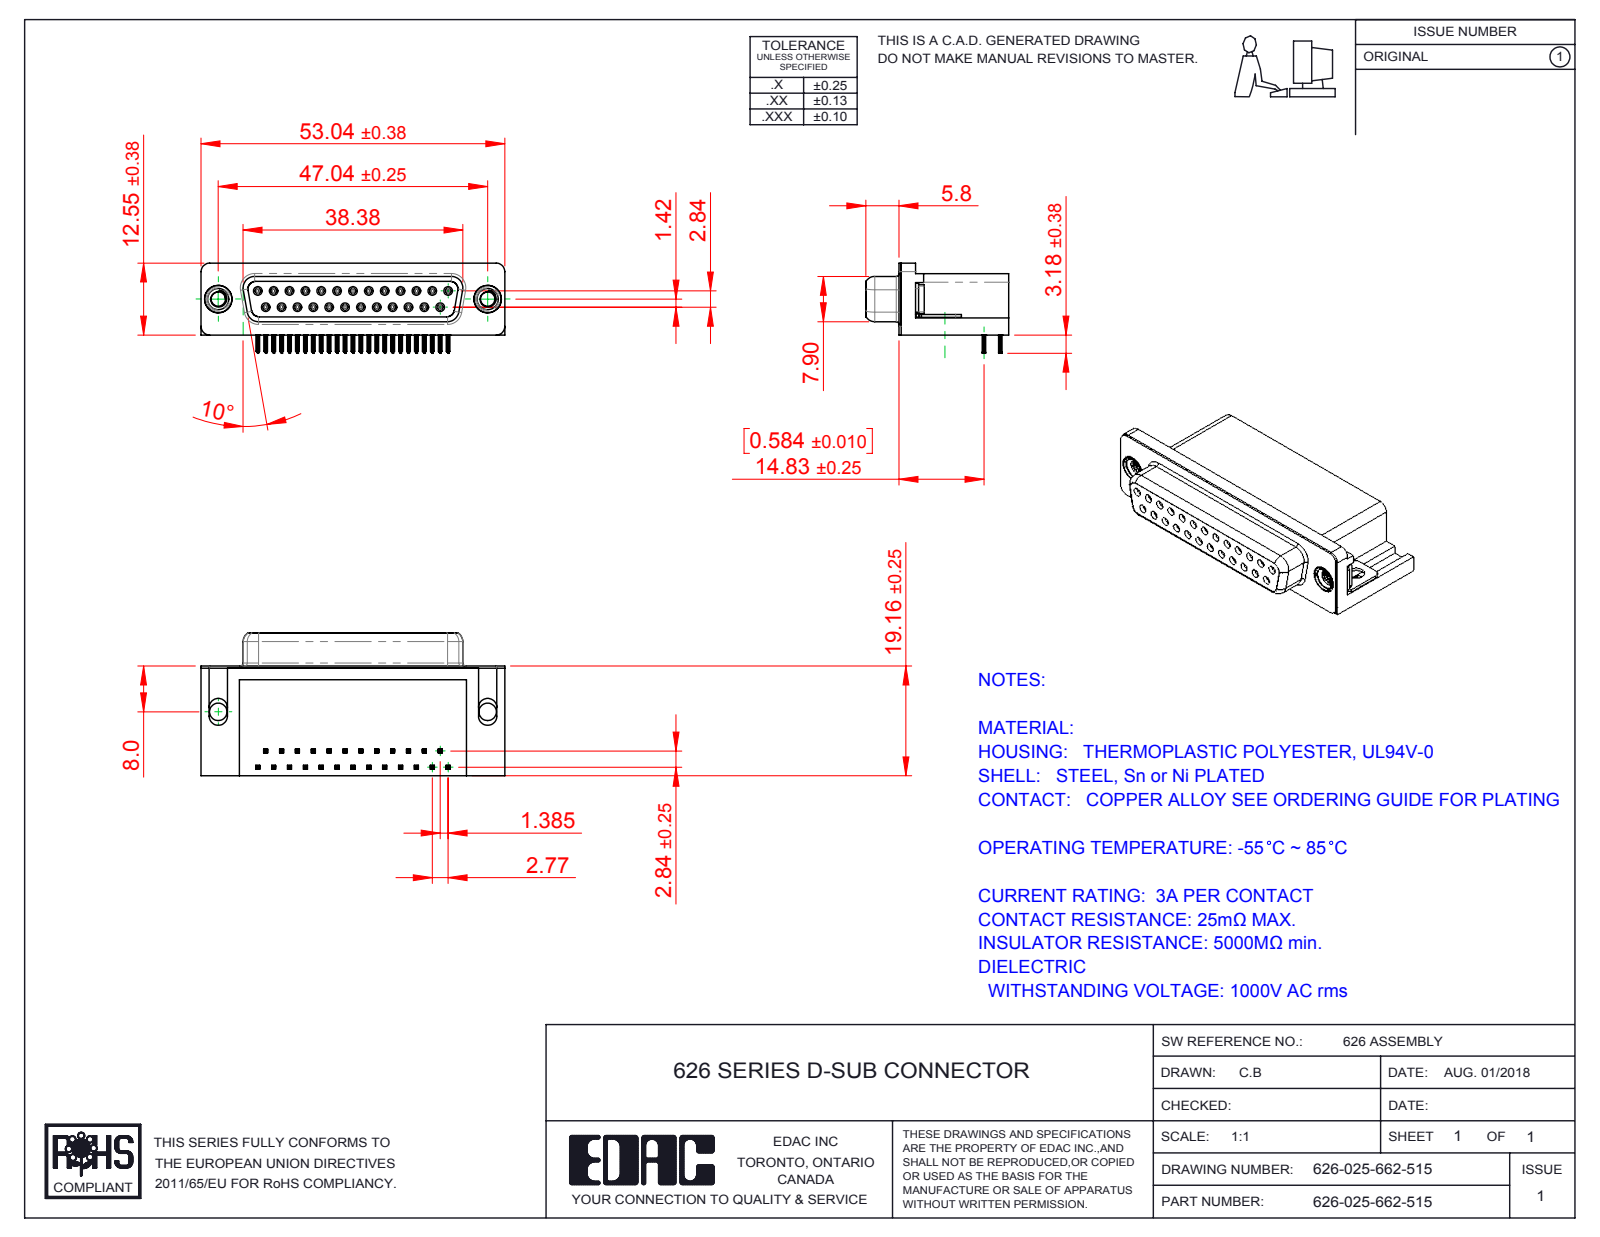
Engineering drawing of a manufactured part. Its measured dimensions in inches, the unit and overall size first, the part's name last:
Units: inches
Overall size (bounding box): 2.088 × 0.983 × 0.619
Round holes (diameter × count): ⌀0.031 ×25, ⌀0.035 ×25, ⌀0.098 ×2, ⌀0.12 ×2, ⌀0.157 ×2, ⌀0.189 ×2, ⌀0.197 ×2
Round bosses / shafts (diameter × count): ⌀0.047 ×25, ⌀0.193 ×2, ⌀0.187 ×2, ⌀0.154 ×2
Partial cylindrical surfaces — rounded edges, fillets, slot ends (radius × count): R0.004 ×200, R0.006 ×100, R0.014 ×50, R0.013 ×25, R0.039 ×18, R0.011 ×12, R0.01 ×8, R0.053 ×8
Main face-to-face distances: 0.016, 0.407, 0.107, 0.739, 0.244, 0.033, 0.369, 0.125, 0.112, 0.014
Hole centre spacings: 0.124, 0.109, 0.218, 0.327, 0.436, 0.198, 0.198, 0.294
Volume: 0.651 in³ · Surface area: 17.6 in²
Bodies: 31 solids, 3850 faces (1722 planar, 924 cylindrical, 1204 other)
Part name (STEP PRODUCT): 626-025-662-515; 626 M3 Threaded Rivet; 626 Contact Bottom; 626 Housing_25 Socket (+3 more)
STEP written by: SolidWorks 2016 (CONFIG_CONTROL_DESIGN)
